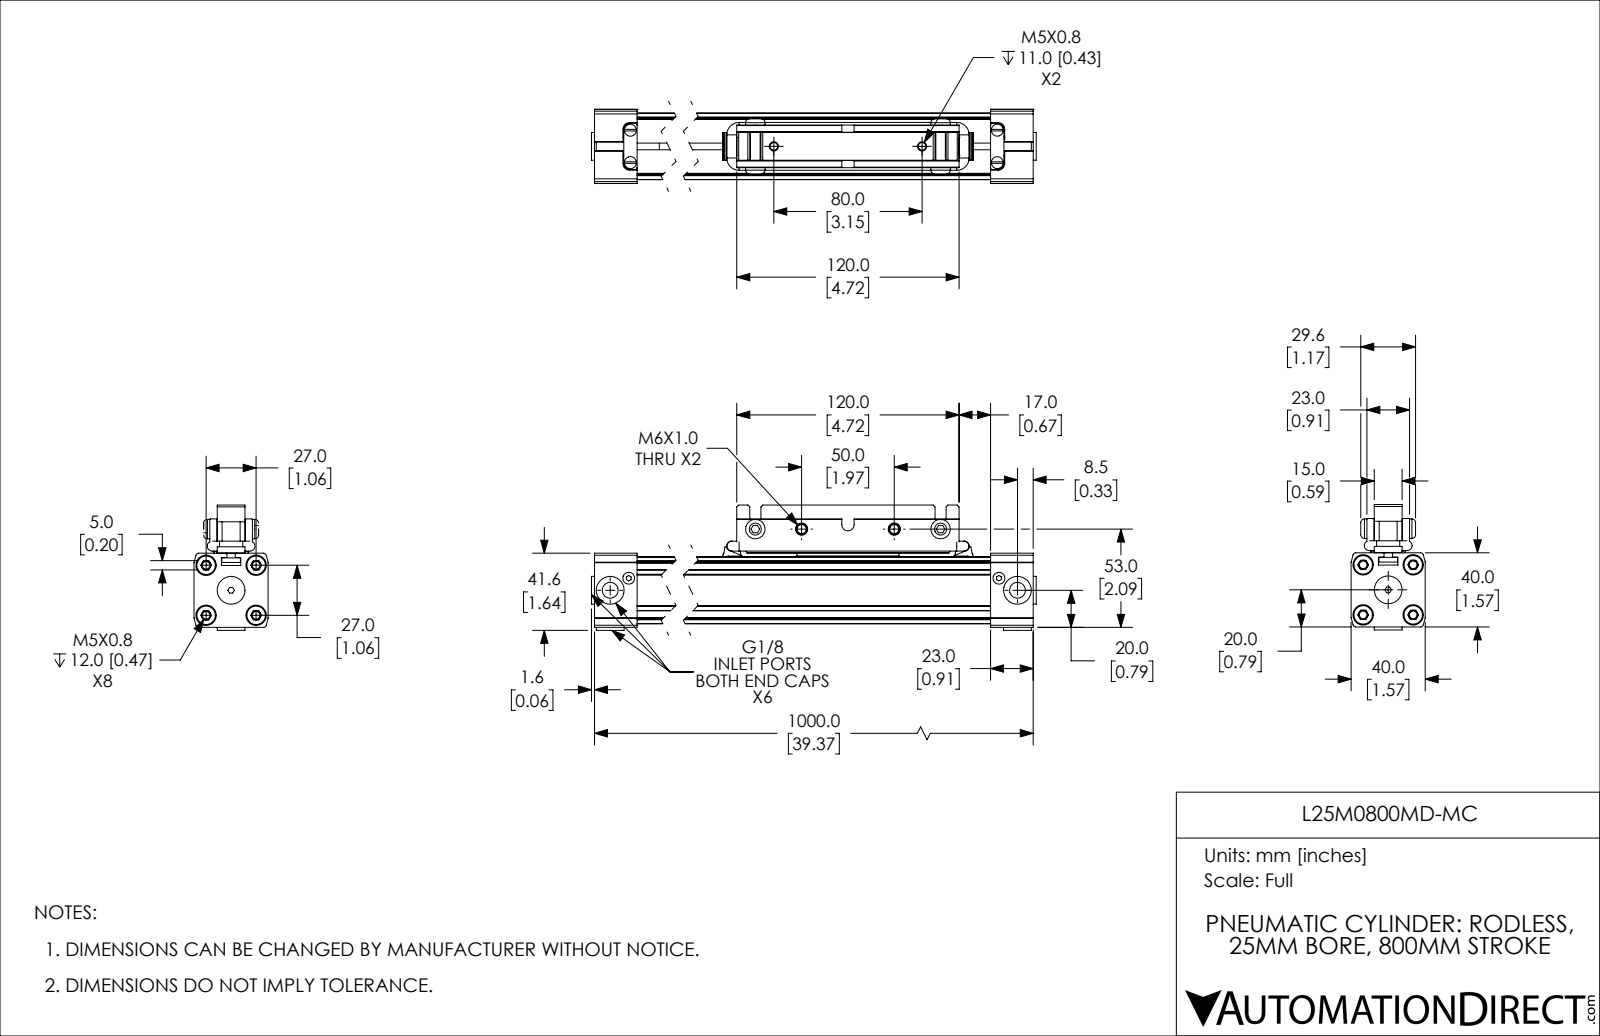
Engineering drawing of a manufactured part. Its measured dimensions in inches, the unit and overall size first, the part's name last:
Units: inches
Overall size (bounding box): 39.499 × 2.663 × 1.575
Round holes (diameter × count): ⌀0.163 ×6, ⌀0.337 ×5, ⌀0.591 ×5, ⌀0.256 ×4, ⌀0.26 ×4, ⌀0.433 ×4, ⌀0.194 ×2, ⌀0.194 ×2, ⌀0.252 ×2, ⌀0.988 ×1
Round bosses / shafts (diameter × count): ⌀0.394 ×4, ⌀0.383 ×3, ⌀0.323 ×3, ⌀0.413 ×2, ⌀0.21 ×2, ⌀0.21 ×2, ⌀0.984 ×1
Partial cylindrical surfaces — rounded edges, fillets, slot ends (radius × count): R0.012 ×28, R0.02 ×14, R0.039 ×14, R0.01 ×12, R0.138 ×8, R0.025 ×6, R0.059 ×6, R0.094 ×6
Main face-to-face distances: 1.413, 1.417, 0.635, 0.777, 0.429, 0.079, 0.335, 0.906, 1.496, 0.224
Hole centre spacings: 0.55, 0.752, 1.063, 38.273, 0.47, 0.689, 0.698, 0.809
Volume: 54.62 in³ · Surface area: 484.8 in²
Bodies: 13 solids, 883 faces (453 planar, 322 cylindrical, 108 other)
Part name (STEP PRODUCT): L25M0800MD-MC; L25M0800MD-MC_BODY; L25M0800MD-MC_PISTON
STEP written by: SolidWorks 2019 (CONFIG_CONTROL_DESIGN)
